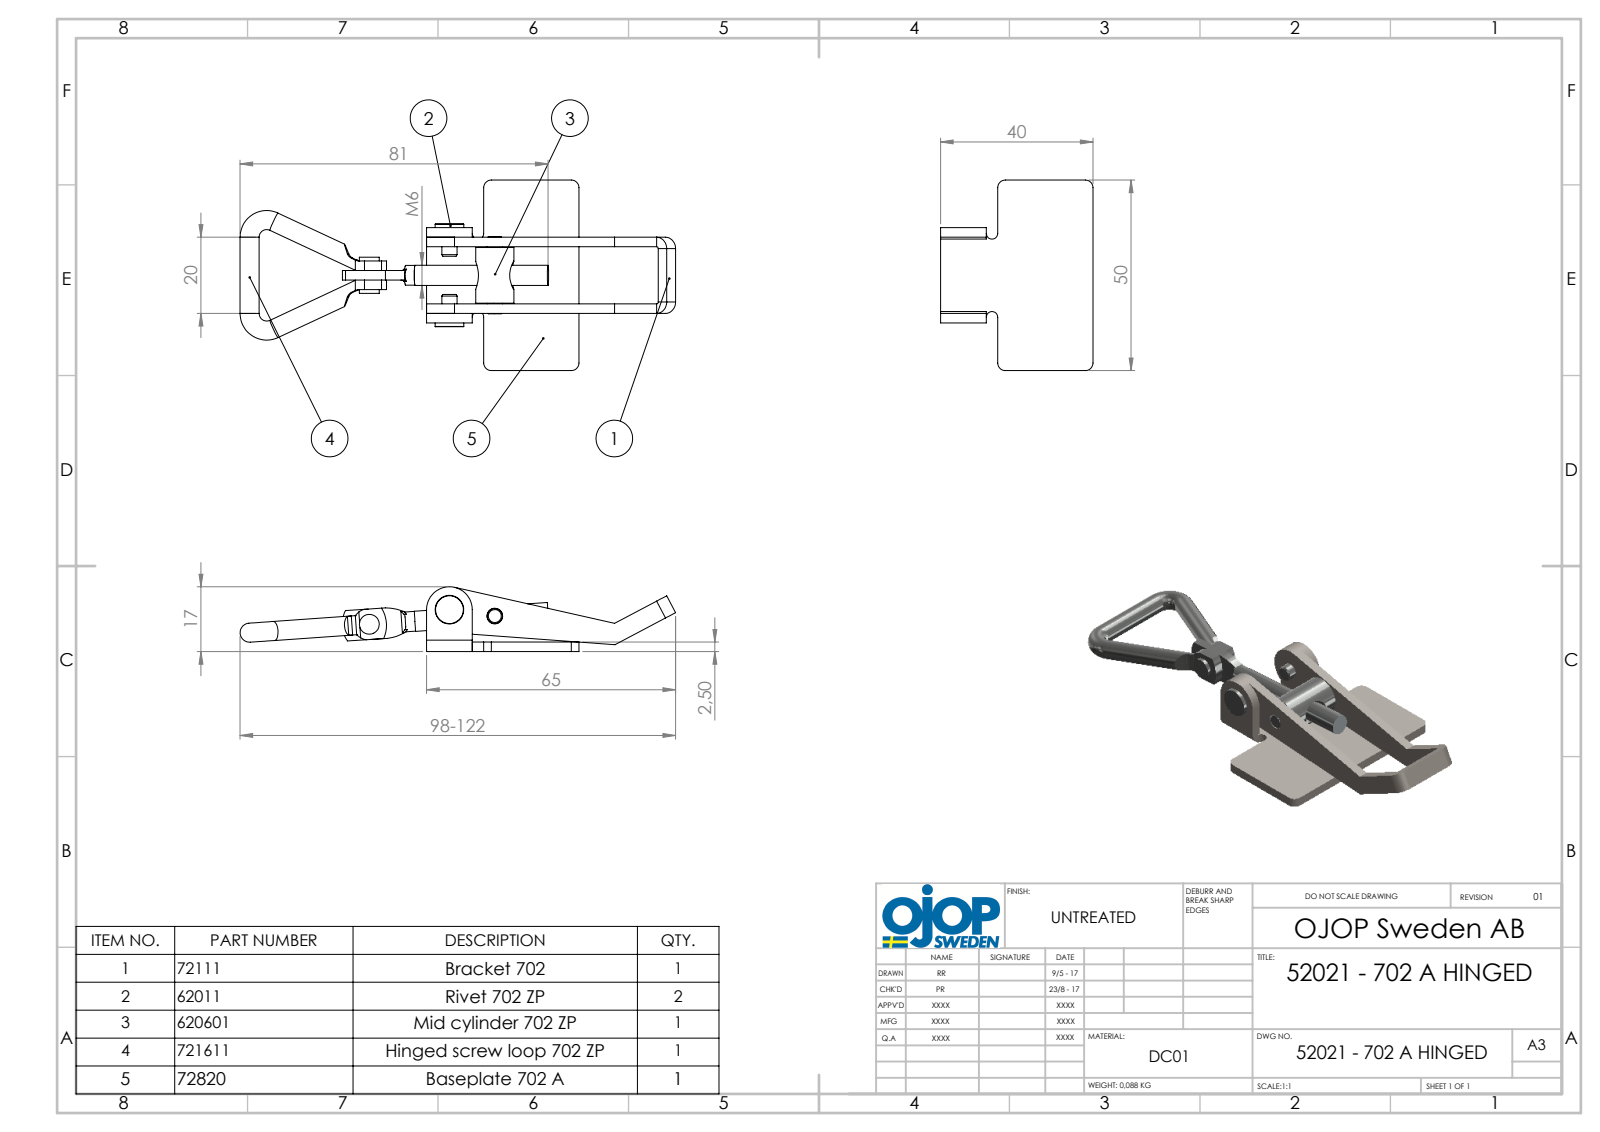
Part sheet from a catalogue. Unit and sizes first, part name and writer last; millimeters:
Units: millimetres
Overall size (bounding box): 115.75 × 50 × 17
Round holes (diameter × count): ⌀4.1 ×3, ⌀5 ×2
Round bosses / shafts (diameter × count): ⌀5 ×3, ⌀4 ×2, ⌀10 ×1, ⌀7.5 ×1, ⌀6 ×1, ⌀5.3 ×1, ⌀5.2 ×1, ⌀5.18 ×1
Partial cylindrical surfaces — rounded edges, fillets, slot ends (radius × count): R2 ×8, R1 ×6, R0.5 ×4, R3 ×4, R1.5 ×2, R6.78 ×2, R12.31 ×2, R3.85 ×1
Main face-to-face distances: 2.5, 17.5, 20, 8.75, 11.25, 15, 5, 13.75, 6.25, 22.5
Hole centre spacings: 12.03, 22.74, 34.5
Volume: 11 812 mm³ · Surface area: 11 549 mm²
Bodies: 8 solids, 201 faces (82 planar, 97 cylindrical, 22 other)
Part name (STEP PRODUCT): 702 - Skruv till ledad M6; 702 - Ring till ledad M6; 702 - Nit till ledad M6; 702 - Ring 702 M6 (+5 more)
STEP written by: SolidWorks 2015 (AUTOMOTIVE_DESIGN)
